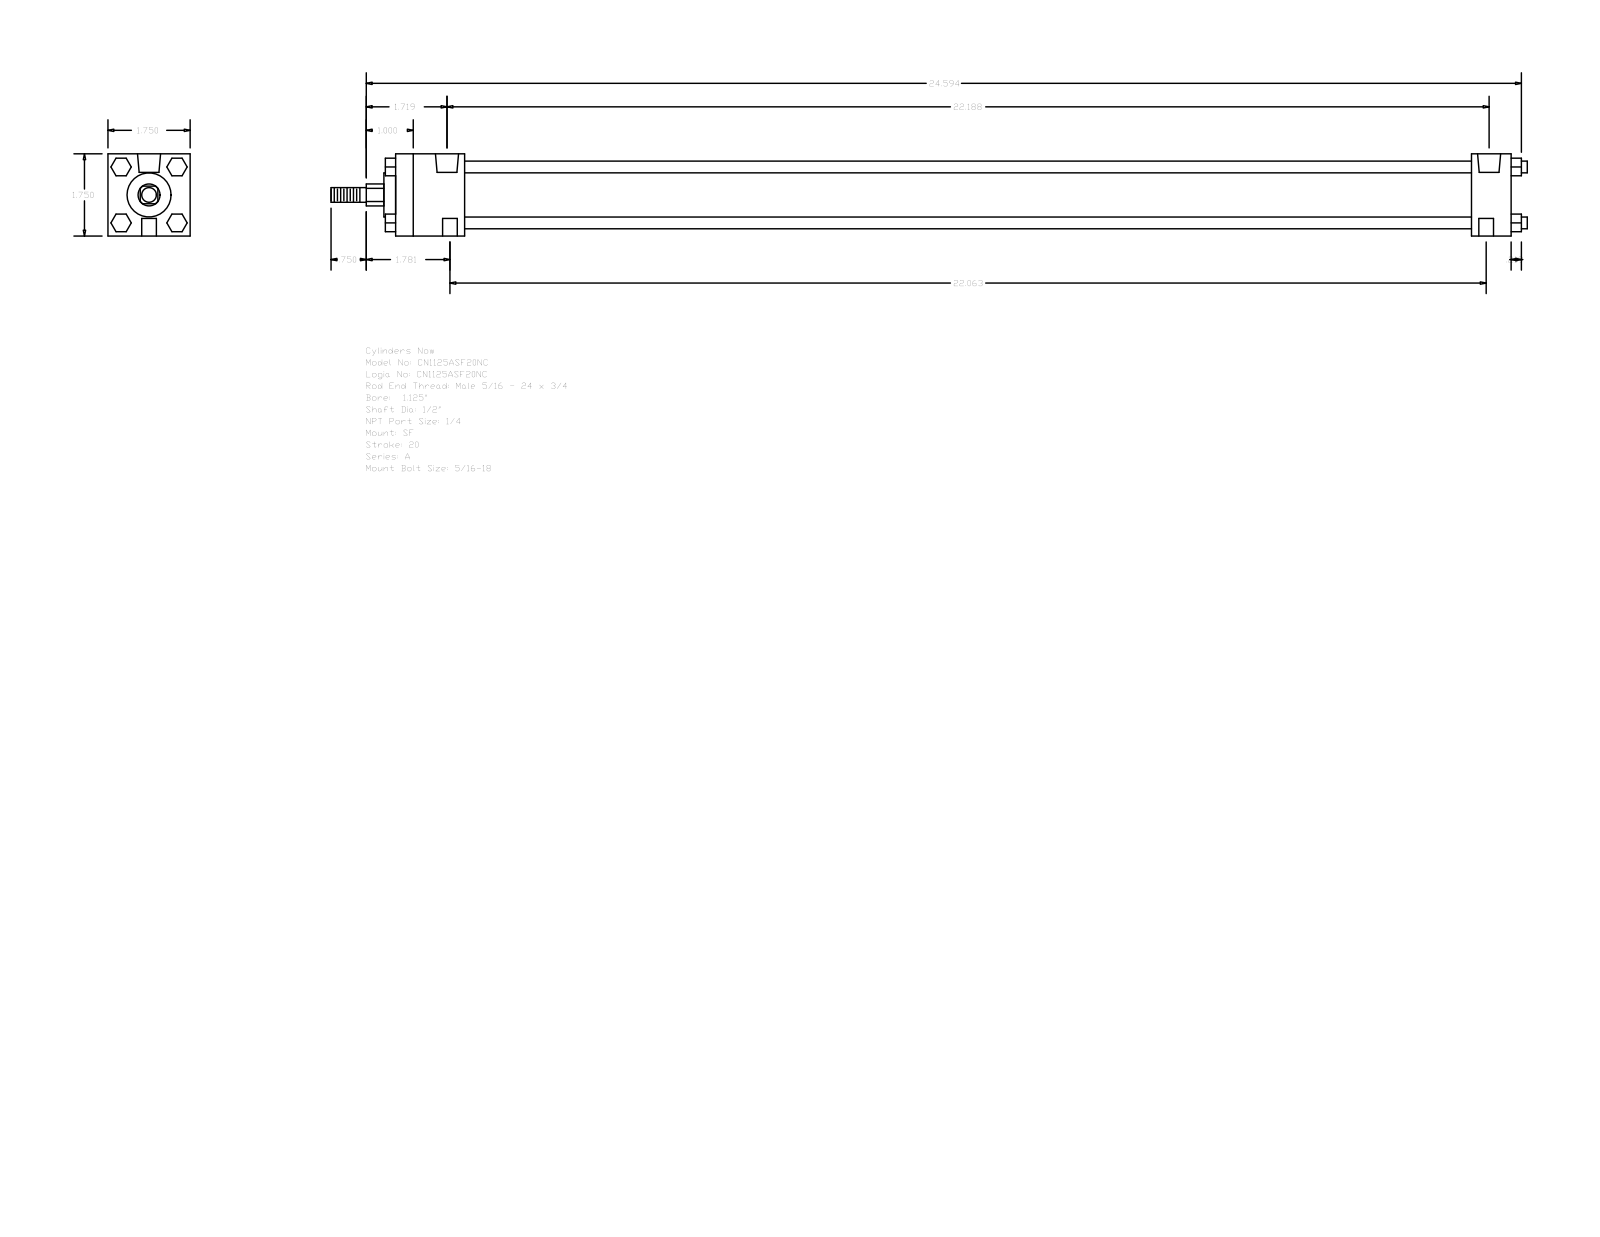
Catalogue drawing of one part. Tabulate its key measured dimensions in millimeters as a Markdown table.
| quantity | value |
| --- | --- |
| part name | A_SF__0112_0.5 |
| STEP written by | GSSL Pune (CONFIG_CONTROL_DESIGN) |
| units | millimeters |
| bodies | 0 solids, 120 faces (92 planar, 28 cylindrical, 0 other) |
| overall size | 646.91 × 44.45 × 44.45 |
| round holes (diameter × count) | 5.56 × 2, 7.94 × 2, 12.49 × 2 |
| round bosses / shafts (diameter × count) | 6.35 × 4, 31.88 × 1, 23.81 × 1, 12.7 × 1, 7.94 × 1 |
| partial cylindrical surfaces (radius × count) | 5.94 × 1 |
| main face-to-face distances | 44.46, 603.24, 581.81, 21.43, 37.3, 544.51, 565.94, 9.53, 5.59, 5.56 |
| hole center spacings | 560.39, 1.58, 1.59, 561.97, 561.98, 563.56 |
